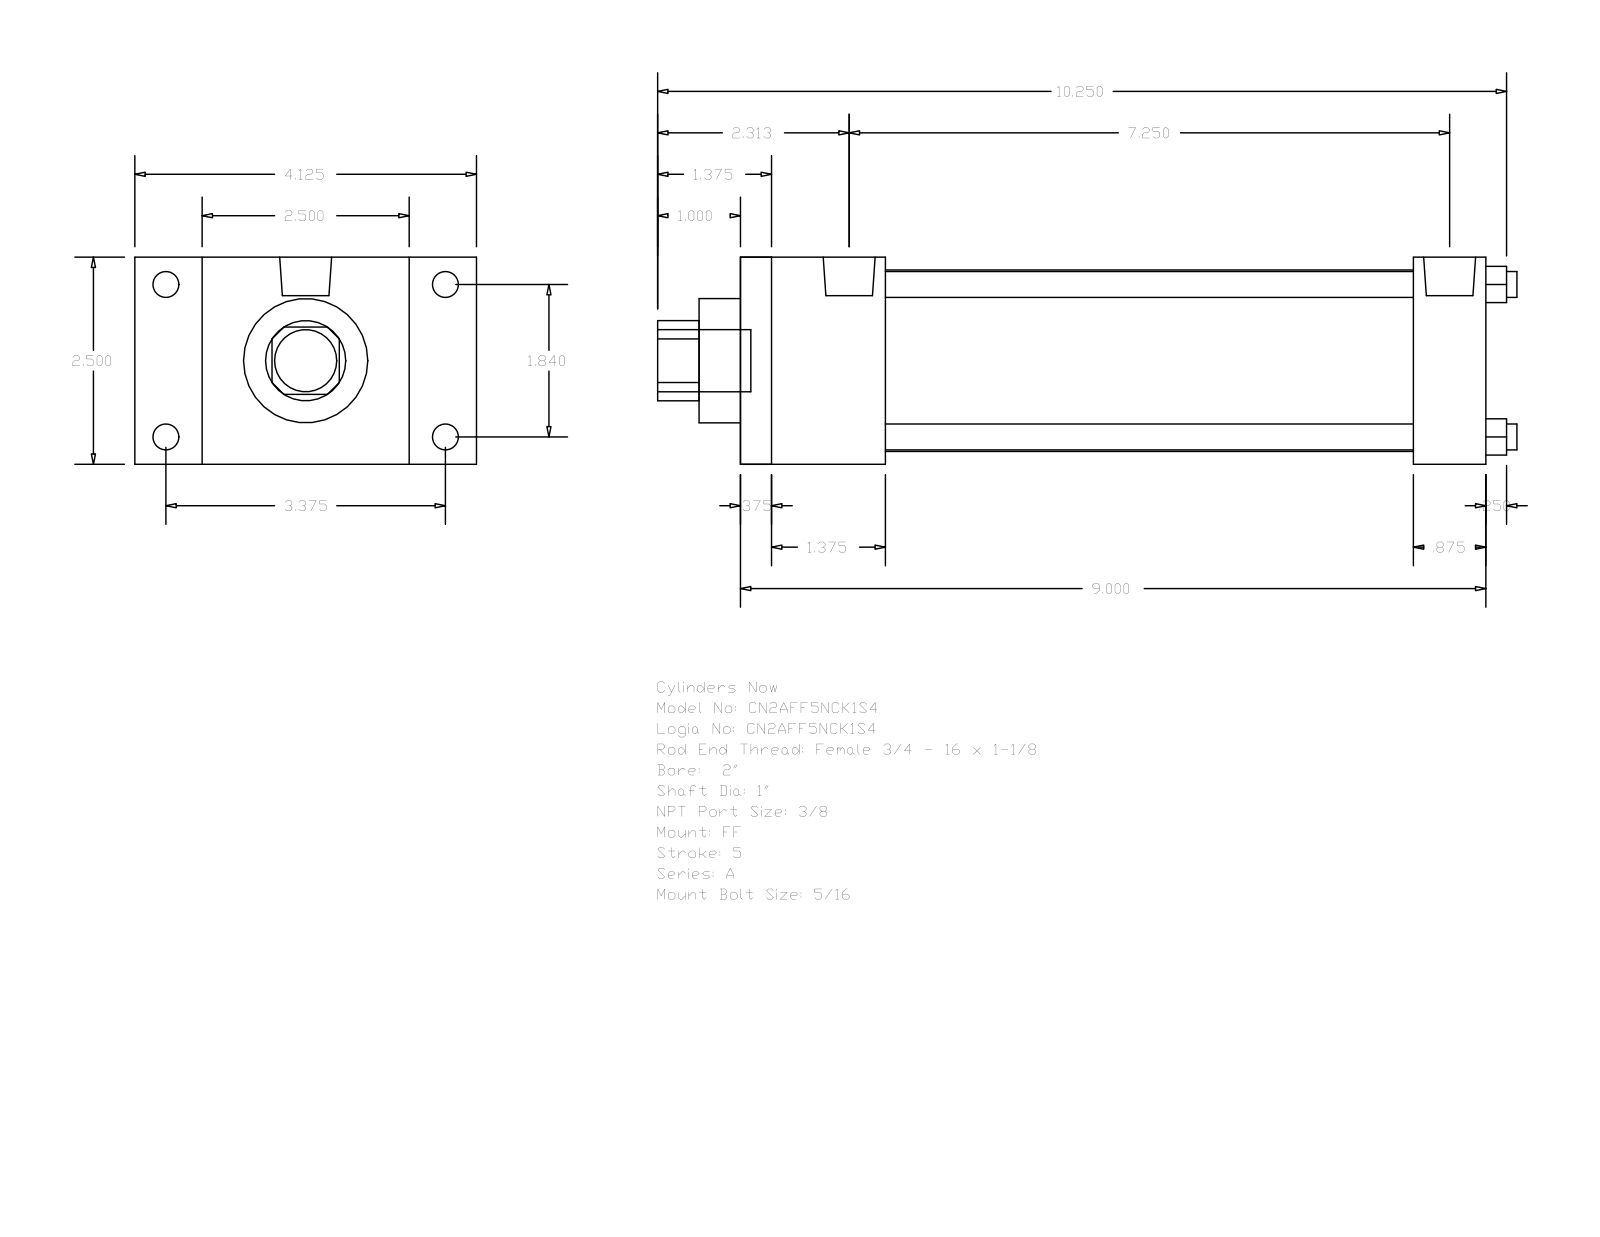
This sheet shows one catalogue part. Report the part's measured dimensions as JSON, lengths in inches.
{"part_name": "A_FF__0200_1", "step_written_by": "GSSL Pune (CONFIG_CONTROL_DESIGN)", "units": "inches", "bodies": {"solids": 0, "faces": 92, "planar": 64, "cylindrical": 28, "other": 0}, "overall_size": [10.375, 4.125, 2.5], "round_holes": [[0.313, 4], [1, 1], [1.5, 1], [2.19, 1]], "round_bosses_or_shafts": [[0.313, 4], [0.219, 4], [0.627, 2], [0.75, 1]], "partial_cylinders_radius": [[0.484, 1]], "face_to_face_distances": [2.5, 9, 8.625, 0.375, 0.875, 0.813, 1.75, 8.125, 1.375, 7.75], "hole_center_spacings": [1.301, 1.84, 2.602]}
